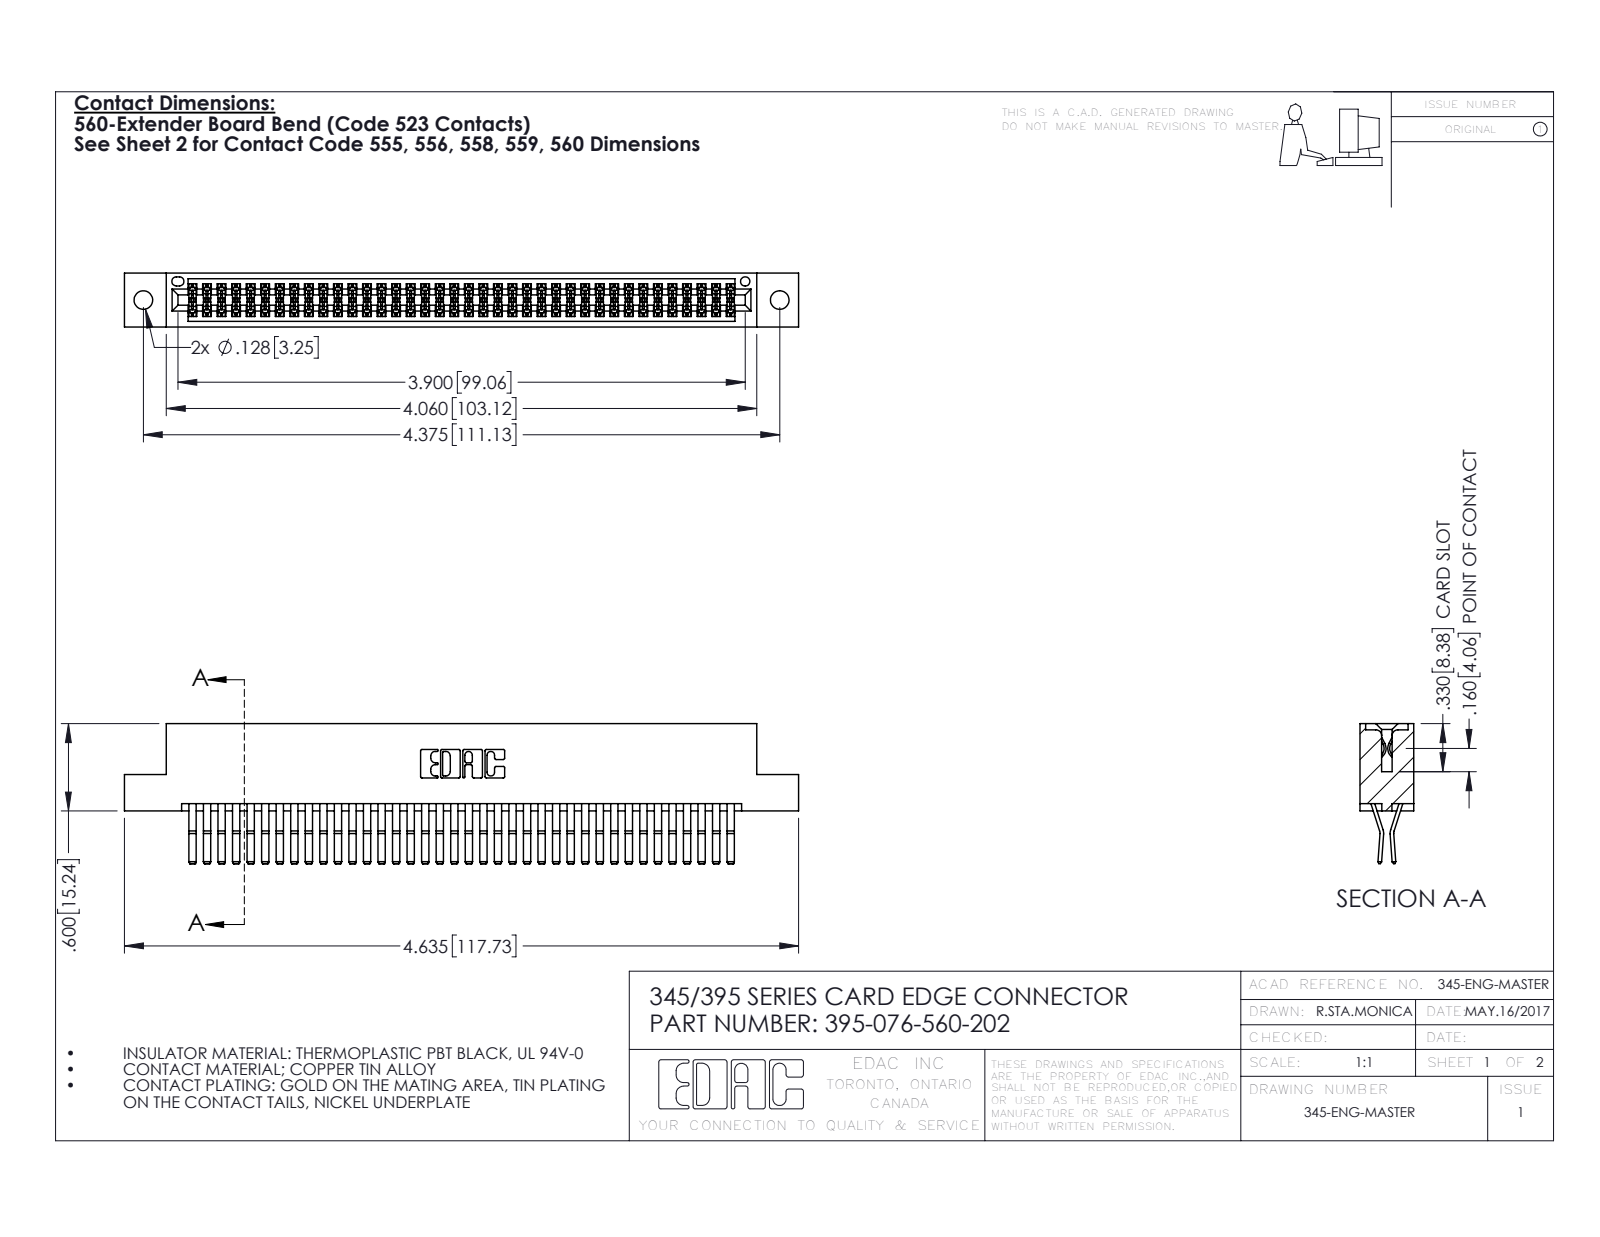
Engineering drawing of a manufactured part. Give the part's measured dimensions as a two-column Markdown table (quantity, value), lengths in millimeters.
| quantity | value |
| --- | --- |
| part name | 345-292-001_560 Tail; 395-076-560-202; 345 Part_Flush Mounting Lugs - 0.128 Dia |
| STEP written by | SolidWorks 2016 (CONFIG_CONTROL_DESIGN) |
| units | millimeters |
| bodies | 77 solids, 4078 faces (2588 planar, 1490 cylindrical, 0 other) |
| overall size | 117.7 × 24.4 × 9.4 |
| volume | 11 900 mm³ |
| surface area | 18 460 mm² |
| round holes (diameter × count) | 3.3 × 2, 1.6 × 1 |
| partial cylindrical surfaces (radius × count) | 0.2 × 114, 0.3 × 22, 0.2 × 6, 0.8 × 6, 0.7 × 3, 0.3 × 2, 0.4 × 2, 0.5 × 2 |
| main face-to-face distances | 0.6, 7.6, 1.8, 5.1, 9.4, 2.5, 6.9, 5.7, 4.4, 3.8 |
| hole center spacings | 6.9, 105.1, 111.1 |
